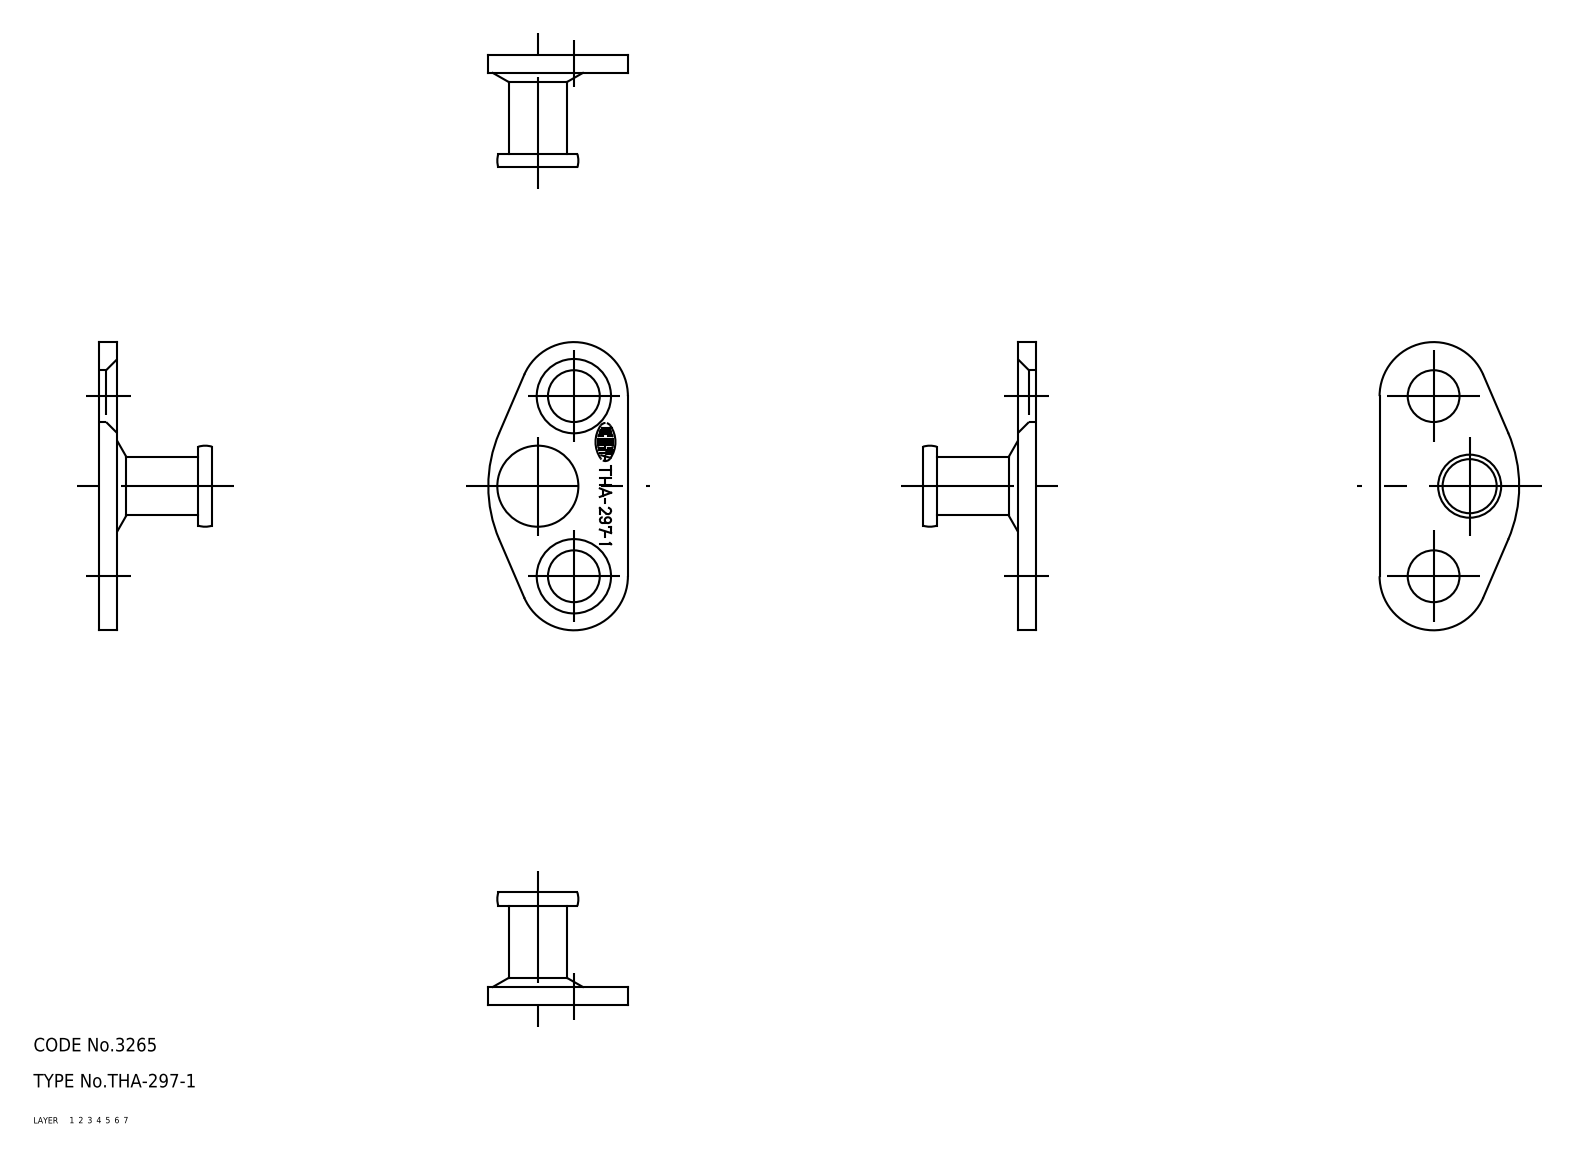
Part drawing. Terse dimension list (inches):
name: pin; base; THA_297_1_720_36
written by: CADfix (AUTOMOTIVE_DESIGN)
unit: in
bodies: 2 solids, 41 faces (0 planar, 0 cylindrical, 41 other)
size: 2.52 × 1.22 × 0.984
volume: 0.52 in³; area: 8.131 in²
